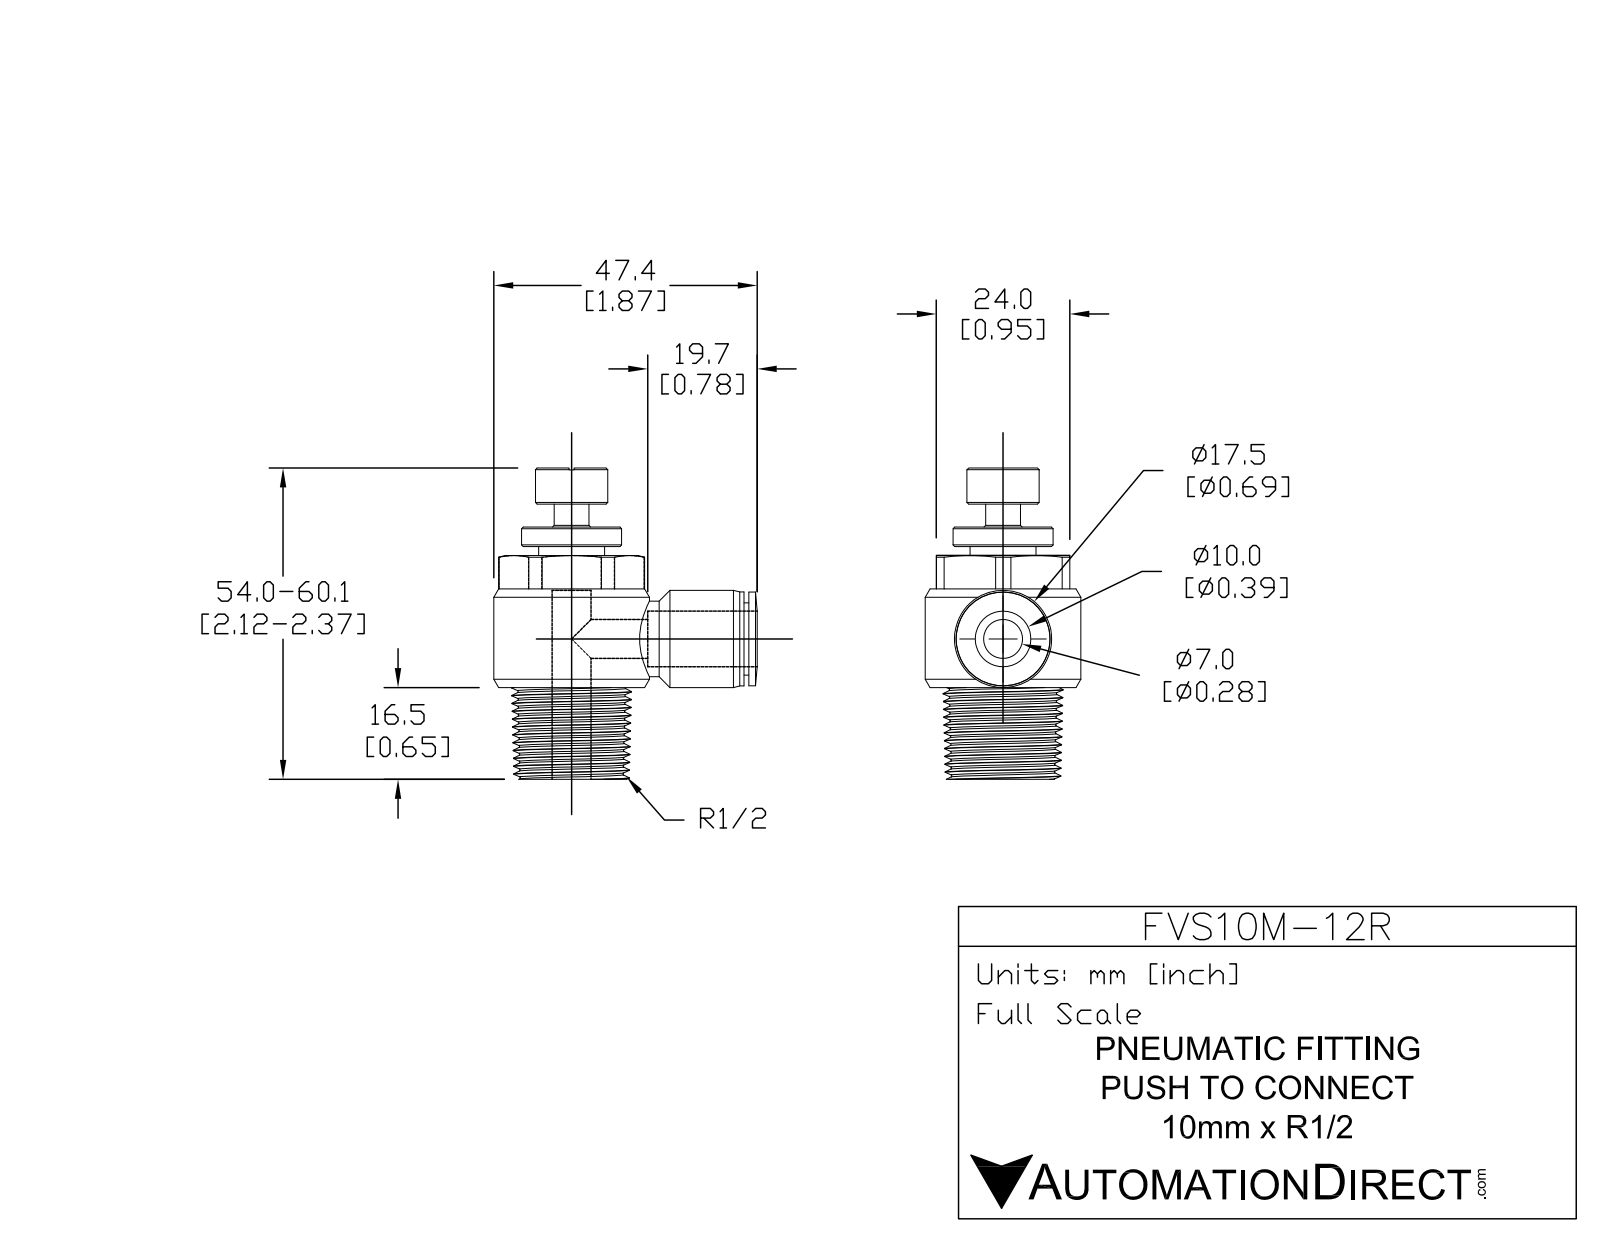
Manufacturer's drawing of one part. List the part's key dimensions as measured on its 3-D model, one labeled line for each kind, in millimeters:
Part name (STEP PRODUCT): FVS10M-12R
STEP written by: SolidWorks 2017 (AUTOMOTIVE_DESIGN)
Units: millimetres
Bodies: 1 solid, 109 faces (27 planar, 33 cylindrical, 49 other)
Overall size (bounding box): 56 × 47.4 × 28
Volume: 21 960 mm³ · Surface area: 9 148 mm²
Round holes (diameter × count): ⌀7 ×2, ⌀10 ×1
Round bosses / shafts (diameter × count): ⌀13 ×2, ⌀28 ×1, ⌀18 ×1, ⌀17.5 ×1, ⌀16.9 ×1, ⌀16.87 ×1, ⌀13.6 ×1, ⌀11.87 ×1
Partial cylindrical surfaces — rounded edges, fillets, slot ends (radius × count): R13.13 ×1
Main face-to-face distances: 40.25, 16.5, 23.75, 45.38, 28.88, 5.13, 41.88, 25.38, 1.63, 3.5
